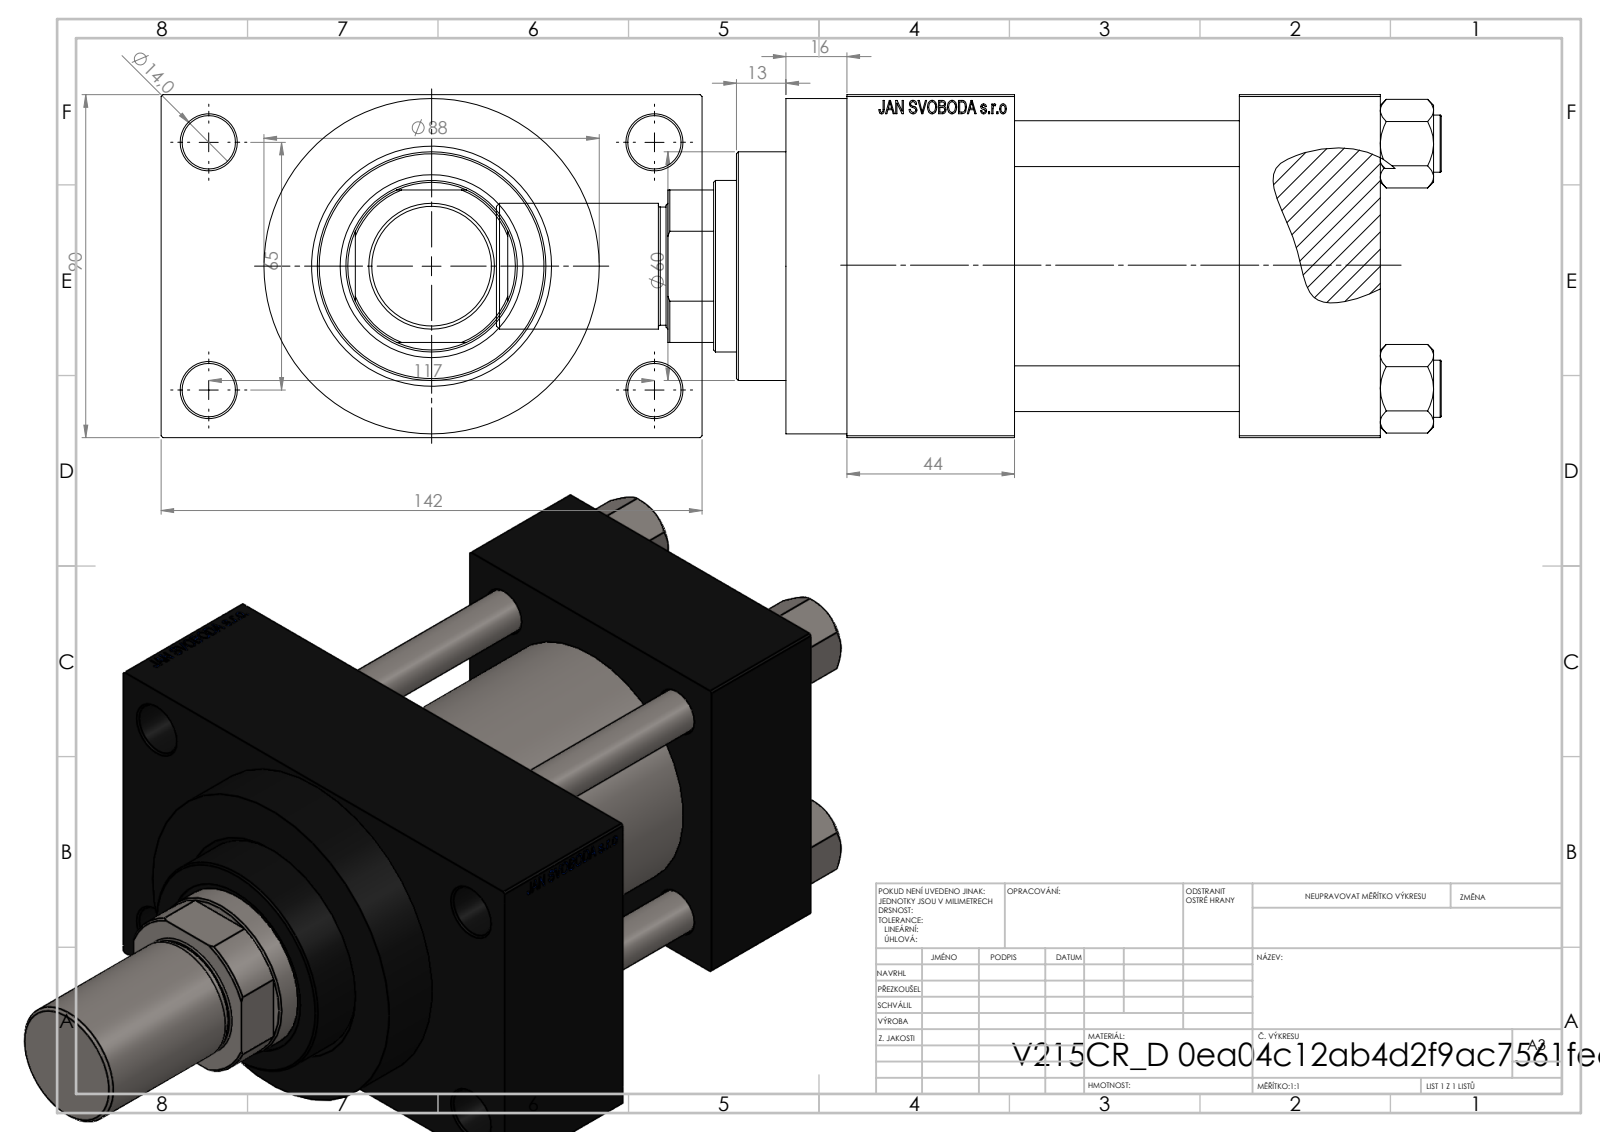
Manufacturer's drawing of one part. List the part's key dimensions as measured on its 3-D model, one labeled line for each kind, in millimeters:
Part name (STEP PRODUCT): V215_VC_A; ROD_END_AH; V215CR_D_Body; NUT_M5_D (+2 more)
STEP written by: SolidWorks 2019 (CONFIG_CONTROL_DESIGN)
Units: millimetres
Bodies: 12 solids, 1116 faces (500 planar, 90 cylindrical, 526 other)
Overall size (bounding box): 248 × 142 × 90
Volume: 1 198 000 mm³ · Surface area: 218 847 mm²
Round holes (diameter × count): ⌀12 ×4, ⌀14 ×4, ⌀7 ×2, ⌀20.96 ×2, ⌀30 ×2, ⌀31.5 ×1, ⌀45 ×1, ⌀48 ×1, ⌀50 ×1, ⌀60 ×1, ⌀63 ×1
Round bosses / shafts (diameter × count): ⌀15 ×4, ⌀88 ×1, ⌀69 ×1, ⌀33 ×1, ⌀31 ×1
Partial cylindrical surfaces — rounded edges, fillets, slot ends (radius × count): R22 ×1
Main face-to-face distances: 90, 59, 37, 96, 26, 140, 103, 44, 116, 156
Hole centre spacings: 26.35, 45.47, 64.3, 66.92, 69.81, 90.65, 111.34, 65
